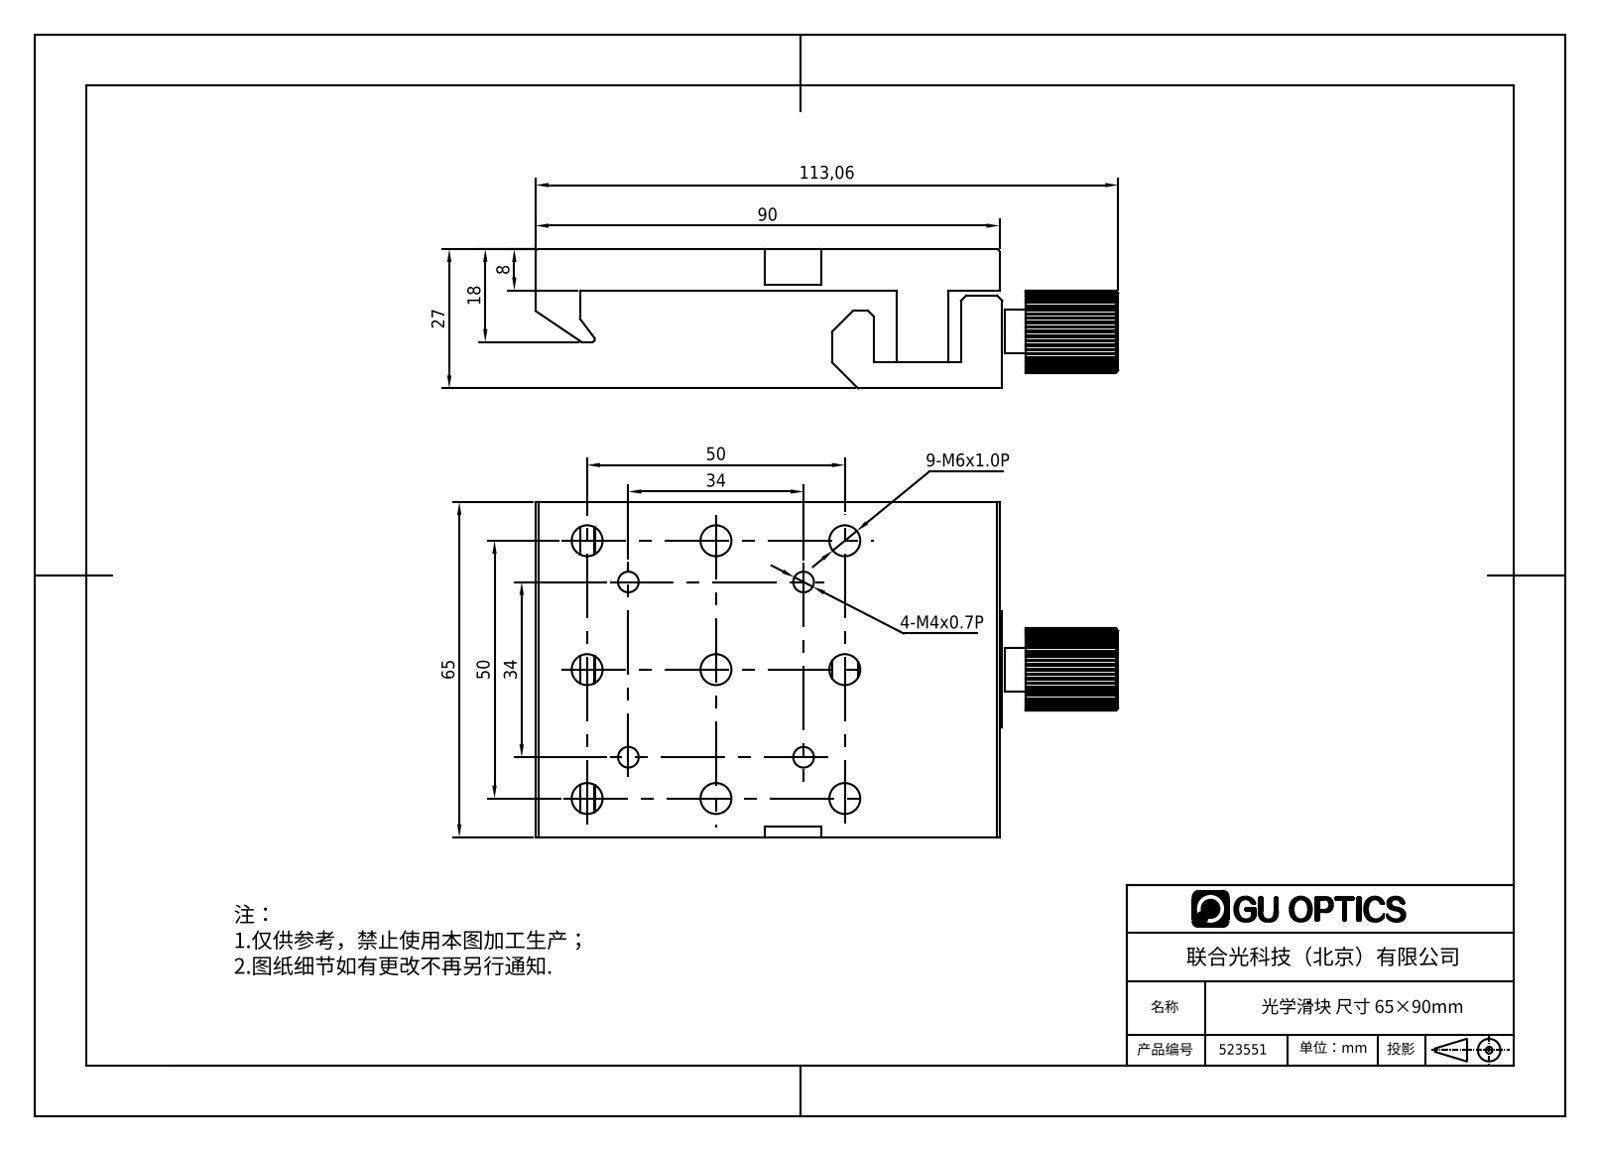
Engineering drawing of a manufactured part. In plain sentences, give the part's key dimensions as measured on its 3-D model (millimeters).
The part is named "CRL-2". Its 3-D file was written by "SolidWorks 2012 (CONFIG_CONTROL_DESIGN)". It is 0 solids with 216 faces: 142 planar, 73 cylindrical and 1 other. Overall it measures 113.06 by 65 by 27 millimeters. Round holes: 9 of diameter 6, 4 of diameter 4. Round bosses or shafts: 1 of diameter 8.5. Partial cylindrical surfaces (rounded edges, fillets, slot ends): 3 of radius 0.5, 1 of radius 8. The main face-to-face distances are 8, 10, 14, 22, 65, 70, 80, 21.25, 43.75, 5. The hole center spacings are 25, 18.79, 35.36, 42.76, 45.31, 55.9, 50, 11.31.
